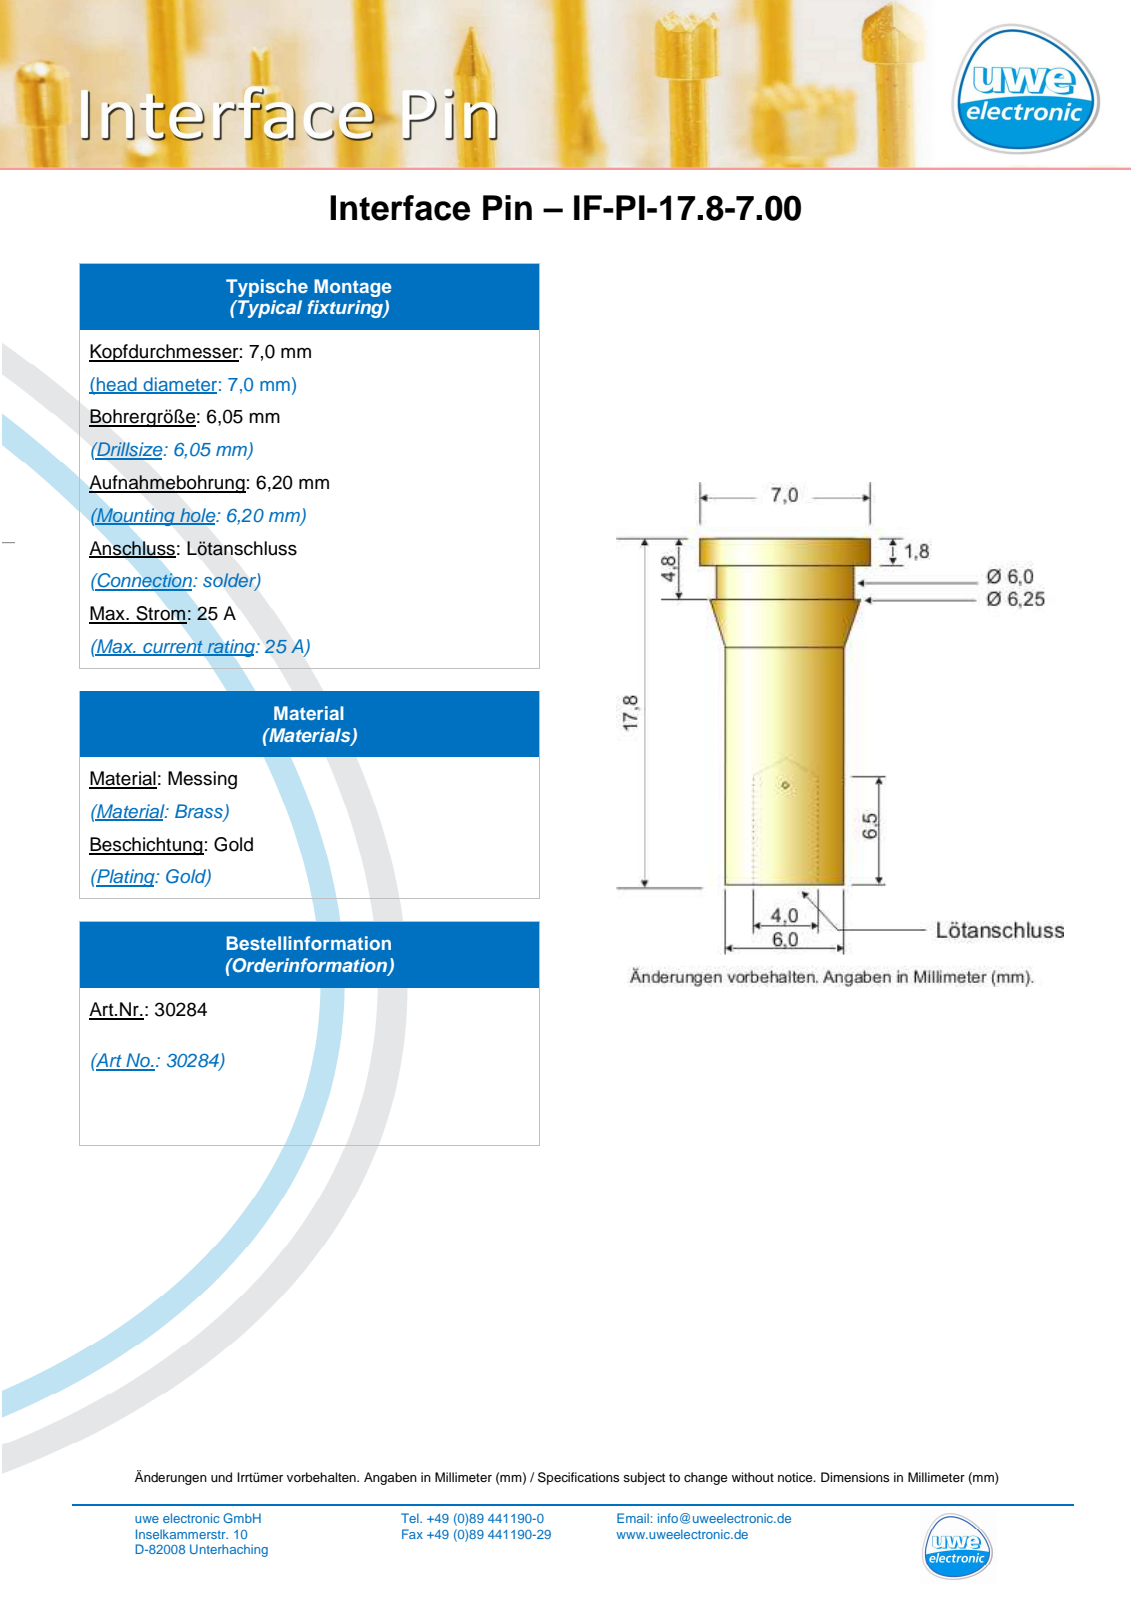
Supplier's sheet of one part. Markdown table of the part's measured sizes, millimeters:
| quantity | value |
| --- | --- |
| part name | IF-PI-17.8-7.00 |
| STEP written by | SolidWorks 2020 (AUTOMOTIVE_DESIGN) |
| units | millimeters |
| bodies | 1 solid, 16 faces (4 planar, 8 cylindrical, 4 other) |
| overall size | 17.8 × 7 × 7 |
| volume | 437 mm³ |
| surface area | 505 mm² |
| round holes (diameter × count) | 4 × 1 |
| round bosses / shafts (diameter × count) | 7 × 1, 6 × 1 |
| main face-to-face distances | 17.8, 16, 1.8, 13, 3, 4.8 |
